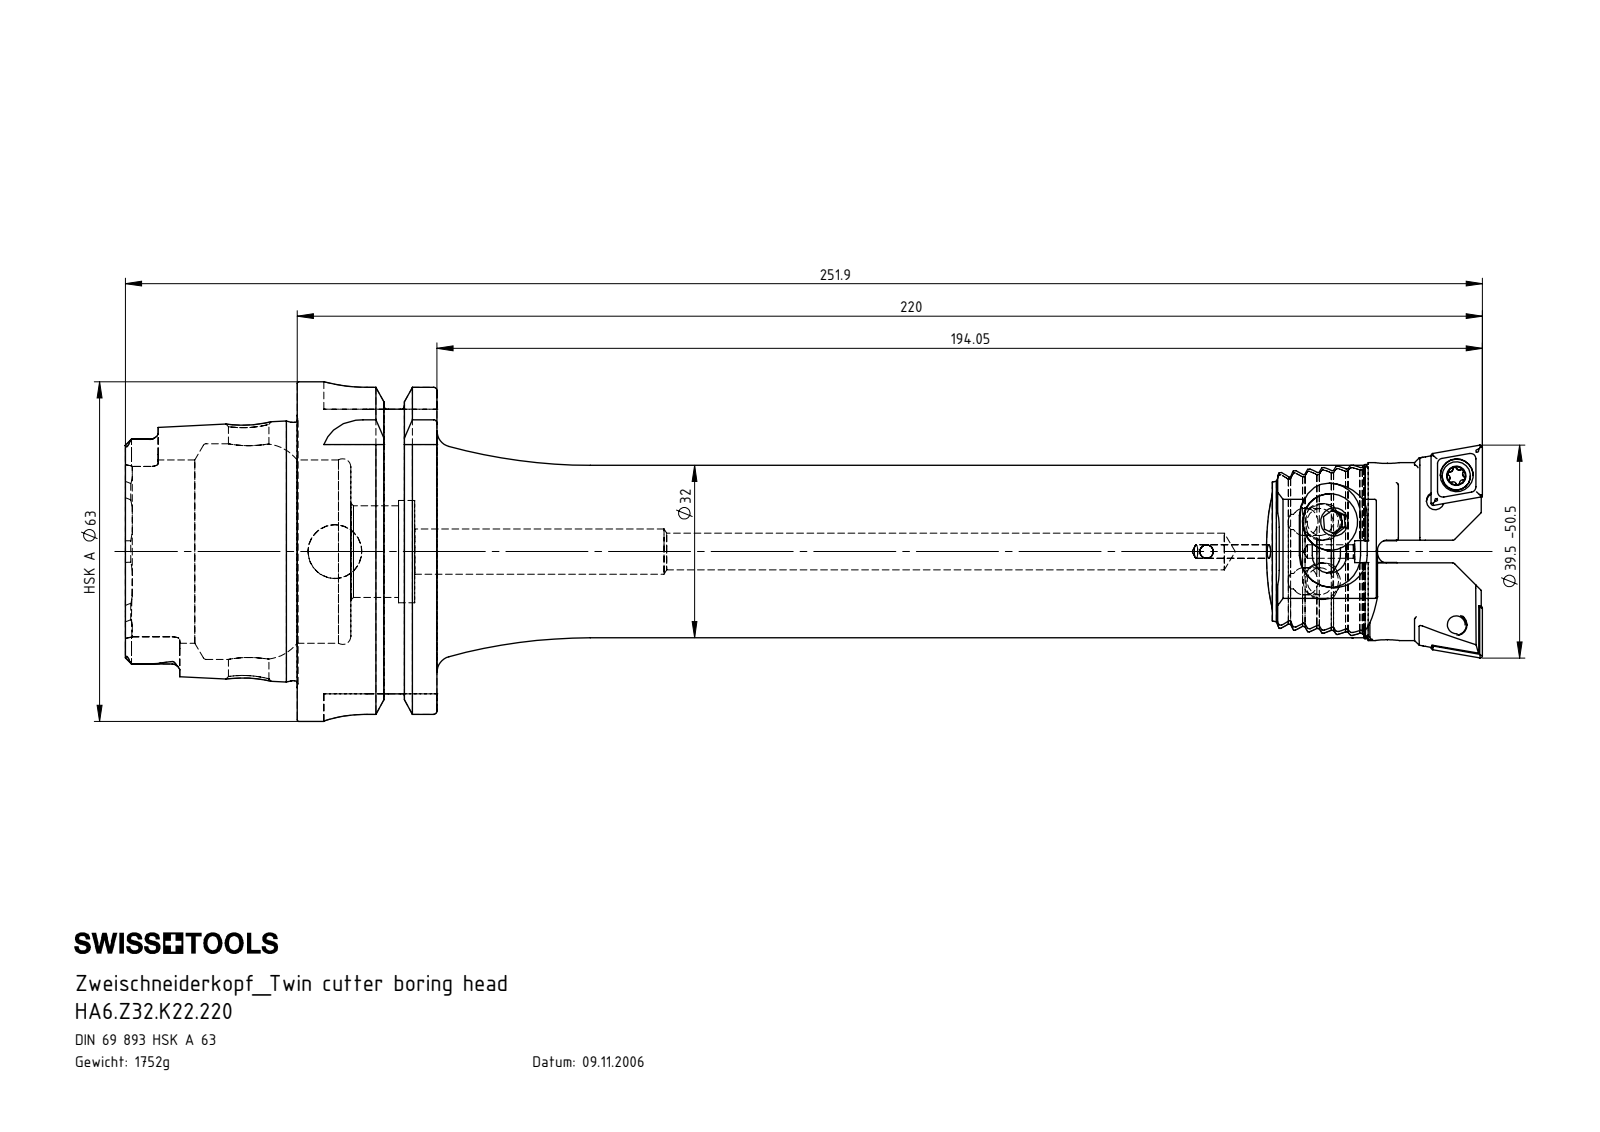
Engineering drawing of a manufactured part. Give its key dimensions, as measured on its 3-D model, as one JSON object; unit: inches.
{"part_name": "Z32-xxx.001.021_B; WCB-ER2.001.009_A; CCMT09T304; Z32-ER3.001.013_A (+5 more)", "step_written_by": "SolidWorks 2022 (CONFIG_CONTROL_DESIGN)", "units": "inches", "bodies": {"solids": 11, "faces": 860, "planar": 345, "cylindrical": 246, "other": 269}, "overall_size": [9.917, 2.48, 2.48], "volume_in3": 13.62, "surface_area_in2": 82.04, "round_holes": [[0.098, 4], [0.13, 4], [0.268, 3], [0.063, 2], [0.173, 2], [0.197, 2], [0.24, 2], [0.079, 1], [0.138, 1], [0.295, 1], [0.331, 1], [0.394, 1]], "round_bosses_or_shafts": [[0.157, 3], [0.413, 2], [0.236, 2], [0.207, 2], [2.48, 1], [2.163, 1], [1.887, 1], [1.26, 1]], "partial_cylinders_radius": [[0.02, 16], [0.008, 14], [0.008, 12], [0.013, 12], [0.023, 12], [0.055, 6], [0.079, 4], [0.113, 4]], "face_to_face_distances": [0.094, 1.022, 0.187, 0.63, 0.375, 0.281, 0.095, 0.092, 0.281, 0.392], "hole_center_spacings": [0.239, 0.244, 0.354, 0.954, 0.958, 1.128, 8.42, 0.684]}
